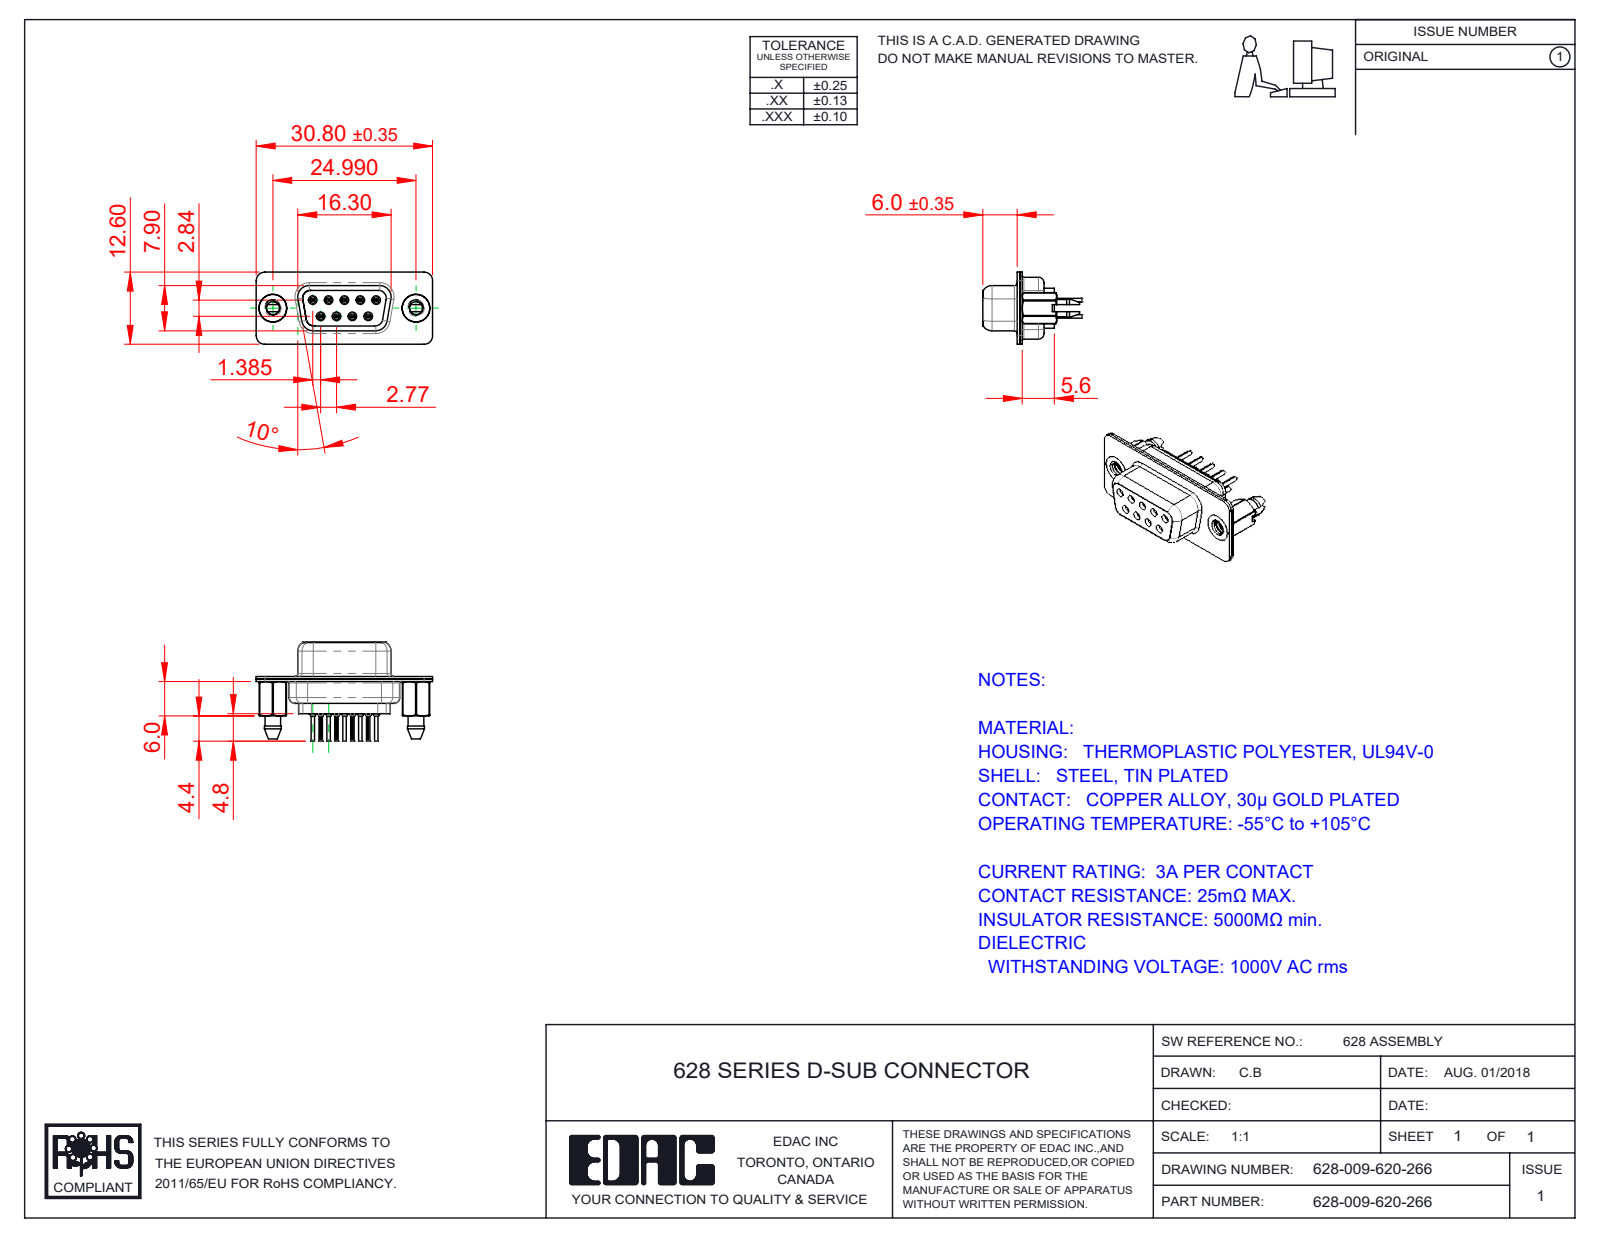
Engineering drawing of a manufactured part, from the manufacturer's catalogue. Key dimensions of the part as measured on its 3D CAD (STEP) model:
Part name (STEP PRODUCT): 628 4-40 Threaded Boardlock_LP; 628 Shell Front_09 Contacts; 628 Contact Row 1_20L; 628 Shell Rear_09 Contacts (+3 more)
STEP written by: SolidWorks 2020 (CONFIG_CONTROL_DESIGN)
Units: millimetres
Bodies: 14 solids, 1496 faces (378 planar, 466 cylindrical, 652 other)
Overall size (bounding box): 30.8 × 17.3 × 12.6
Volume: 1 873 mm³ · Surface area: 4 799 mm²
Round holes (diameter × count): ⌀0.2 ×9, ⌀0.8 ×9, ⌀0.9 ×9, ⌀1.1 ×9, ⌀1.6 ×9, ⌀1.7 ×5, ⌀2.26 ×2, ⌀4 ×2, ⌀4.05 ×2, ⌀4.85 ×2
Round bosses / shafts (diameter × count): ⌀2 ×9, ⌀1.5 ×9, ⌀1.2 ×9, ⌀0.6 ×9, ⌀4.95 ×2, ⌀4.8 ×2
Partial cylindrical surfaces — rounded edges, fillets, slot ends (radius × count): R1.5 ×19, R0.1 ×18, R2 ×12, R0.28 ×9, R1.35 ×6, R1.6 ×6, R0.25 ×4, R0.5 ×4
Main face-to-face distances: 0.45, 0.4, 0.9, 1.9, 8.5, 6.6, 1.4, 0.5, 6.5, 12.5
Hole centre spacings: 3.16, 2.77, 5.54, 5.03, 5.04, 8.31, 7.48, 7.49
